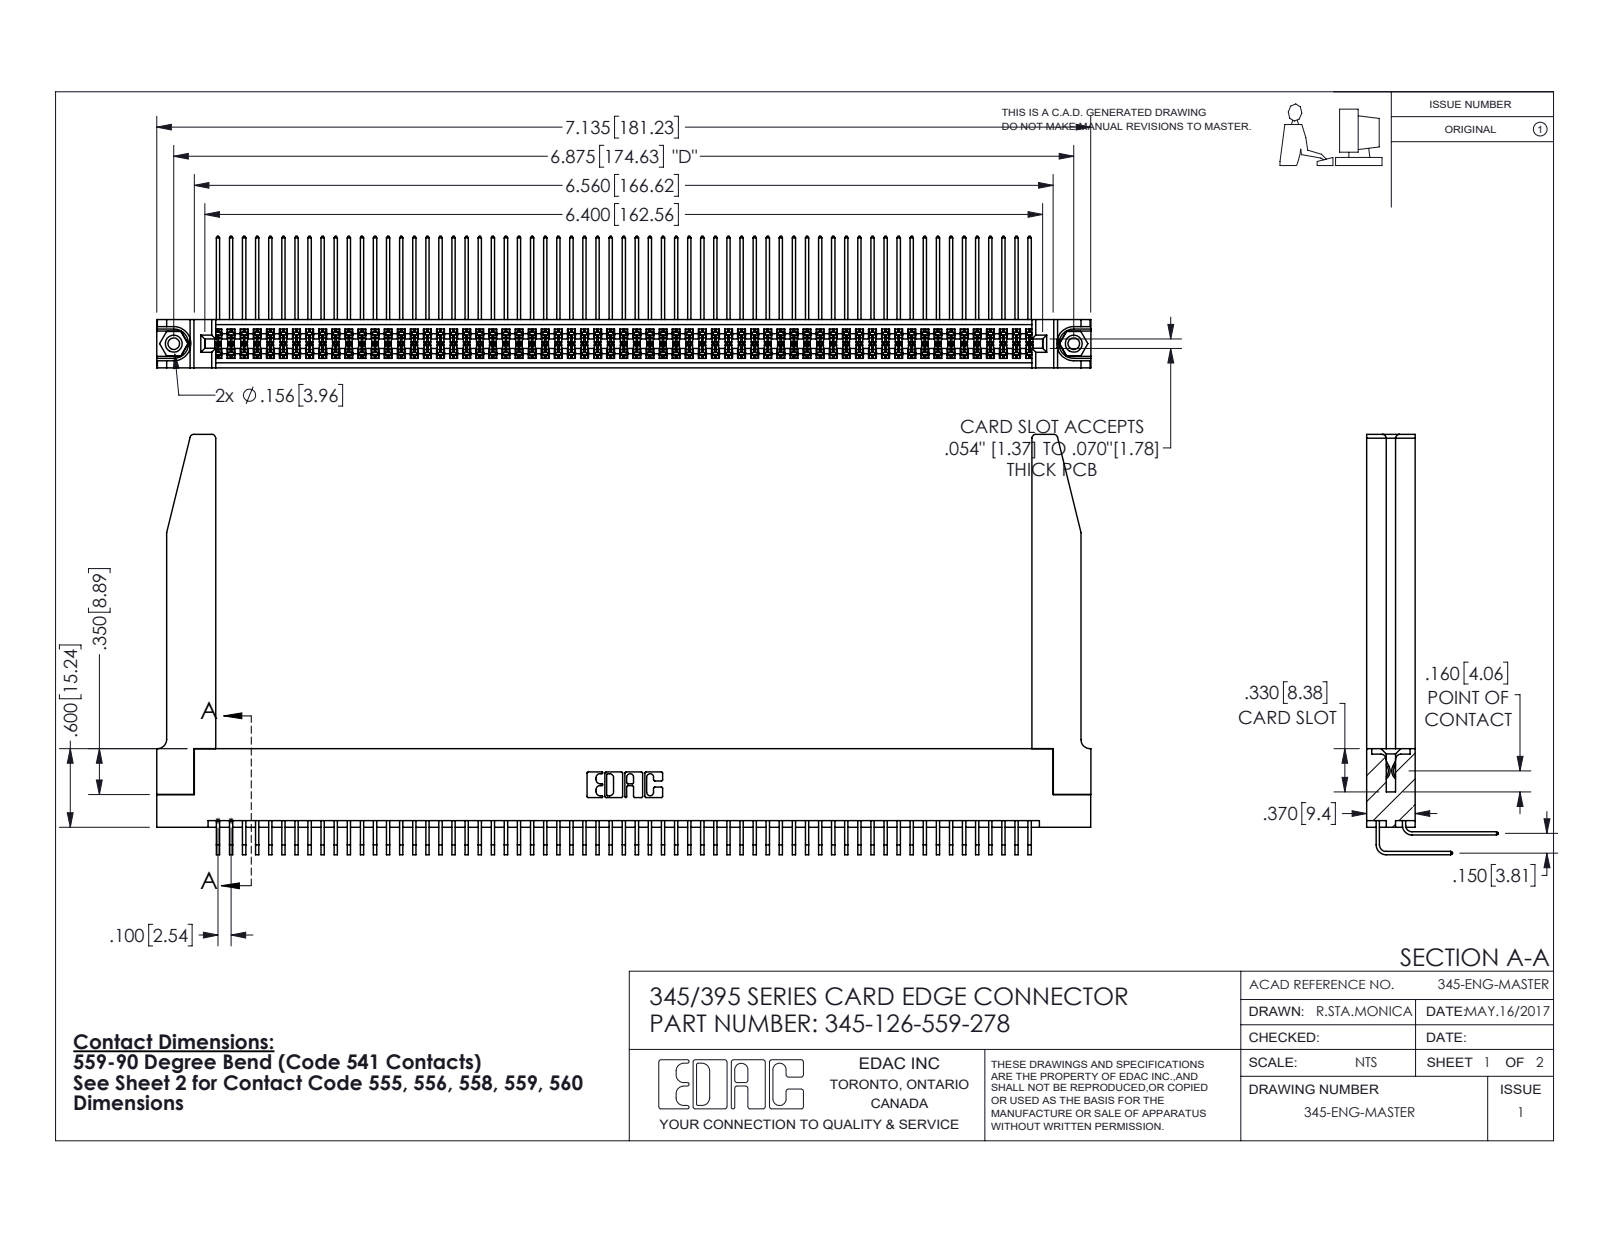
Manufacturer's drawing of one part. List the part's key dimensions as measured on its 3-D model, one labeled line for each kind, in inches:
Part name (STEP PRODUCT): 345-126-559-278; 345-220-078_345-220-078; 345-250-001_345-250-001-102; 345-292-001_559 Tail - 2 (+2 more)
STEP written by: SolidWorks 2016 (CONFIG_CONTROL_DESIGN)
Units: inches
Bodies: 131 solids, 6912 faces (4632 planar, 2228 cylindrical, 52 other)
Overall size (bounding box): 7.136 × 3.209 × 1.005
Volume: 1.605 in³ · Surface area: 58.98 in²
Round holes (diameter × count): ⌀0.089 ×2, ⌀0.125 ×2, ⌀0.156 ×2, ⌀0.064 ×1
Round bosses / shafts (diameter × count): ⌀0.155 ×2
Partial cylindrical surfaces — rounded edges, fillets, slot ends (radius × count): R0.006 ×251, R0.01 ×22, R0.03 ×8, R0.007 ×6, R0.031 ×6, R0.026 ×3, R0.014 ×2, R0.019 ×2
Main face-to-face distances: 0.072, 0.298, 0.37, 0.2, 0.098, 0.272, 0.025, 0.225, 0.175, 0.15
Hole centre spacings: 0.27, 6.639, 6.875
